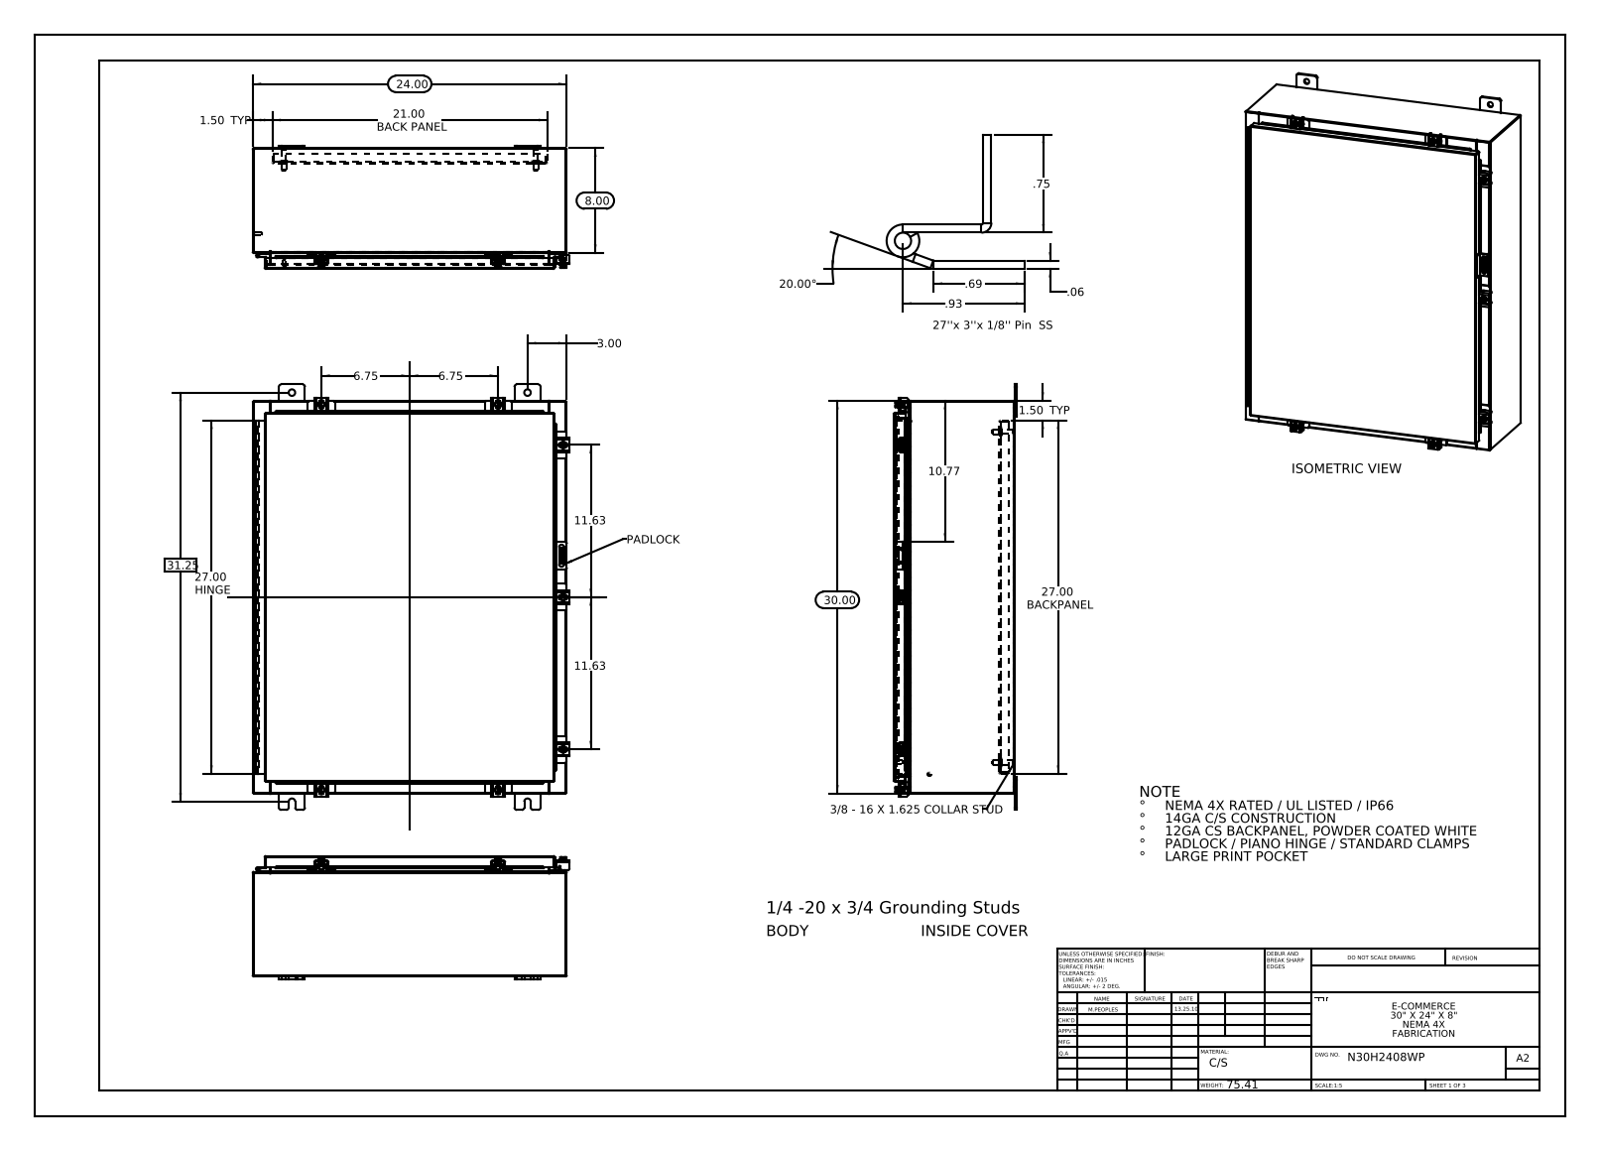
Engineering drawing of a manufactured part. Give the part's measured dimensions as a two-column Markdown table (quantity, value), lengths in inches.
| quantity | value |
| --- | --- |
| part name | N30H2408SSWP Cover; N30H2408SSWP Bottom; N30H2408SSWP Clamp Top; N30H2408SSWP Clamp Bracket (+8 more) |
| STEP written by | SolidWorks 2013 (CONFIG_CONTROL_DESIGN) |
| units | inches |
| bodies | 54 solids, 2016 faces (1062 planar, 838 cylindrical, 116 other) |
| overall size | 32.5 × 24.211 × 9.389 |
| volume | 264.9 in³ |
| surface area | 6 620 in² |
| round holes (diameter × count) | 0.5 × 8, 0.213 × 7, 0.26 × 7, 0.125 × 2 |
| round bosses / shafts (diameter × count) | 0.25 × 8, 0.5 × 7, 0.399 × 7, 0.625 × 4, 0.375 × 4, 0.33 × 4, 0.315 × 2, 0.236 × 2 |
| partial cylindrical surfaces (radius × count) | 0.06 × 34, 0.013 × 27, 0.19 × 24, 0.088 × 21, 0.12 × 14, 0.141 × 14, 0.05 × 11, 0.08 × 10 |
| main face-to-face distances | 0.075, 9.126, 9.051, 9.201, 0.104, 1, 1.075, 8.051, 8.126, 1.179 |
| hole center spacings | 27.501, 31.878, 1.858, 2.277, 2.326, 2.423, 3.561, 3.561 |
